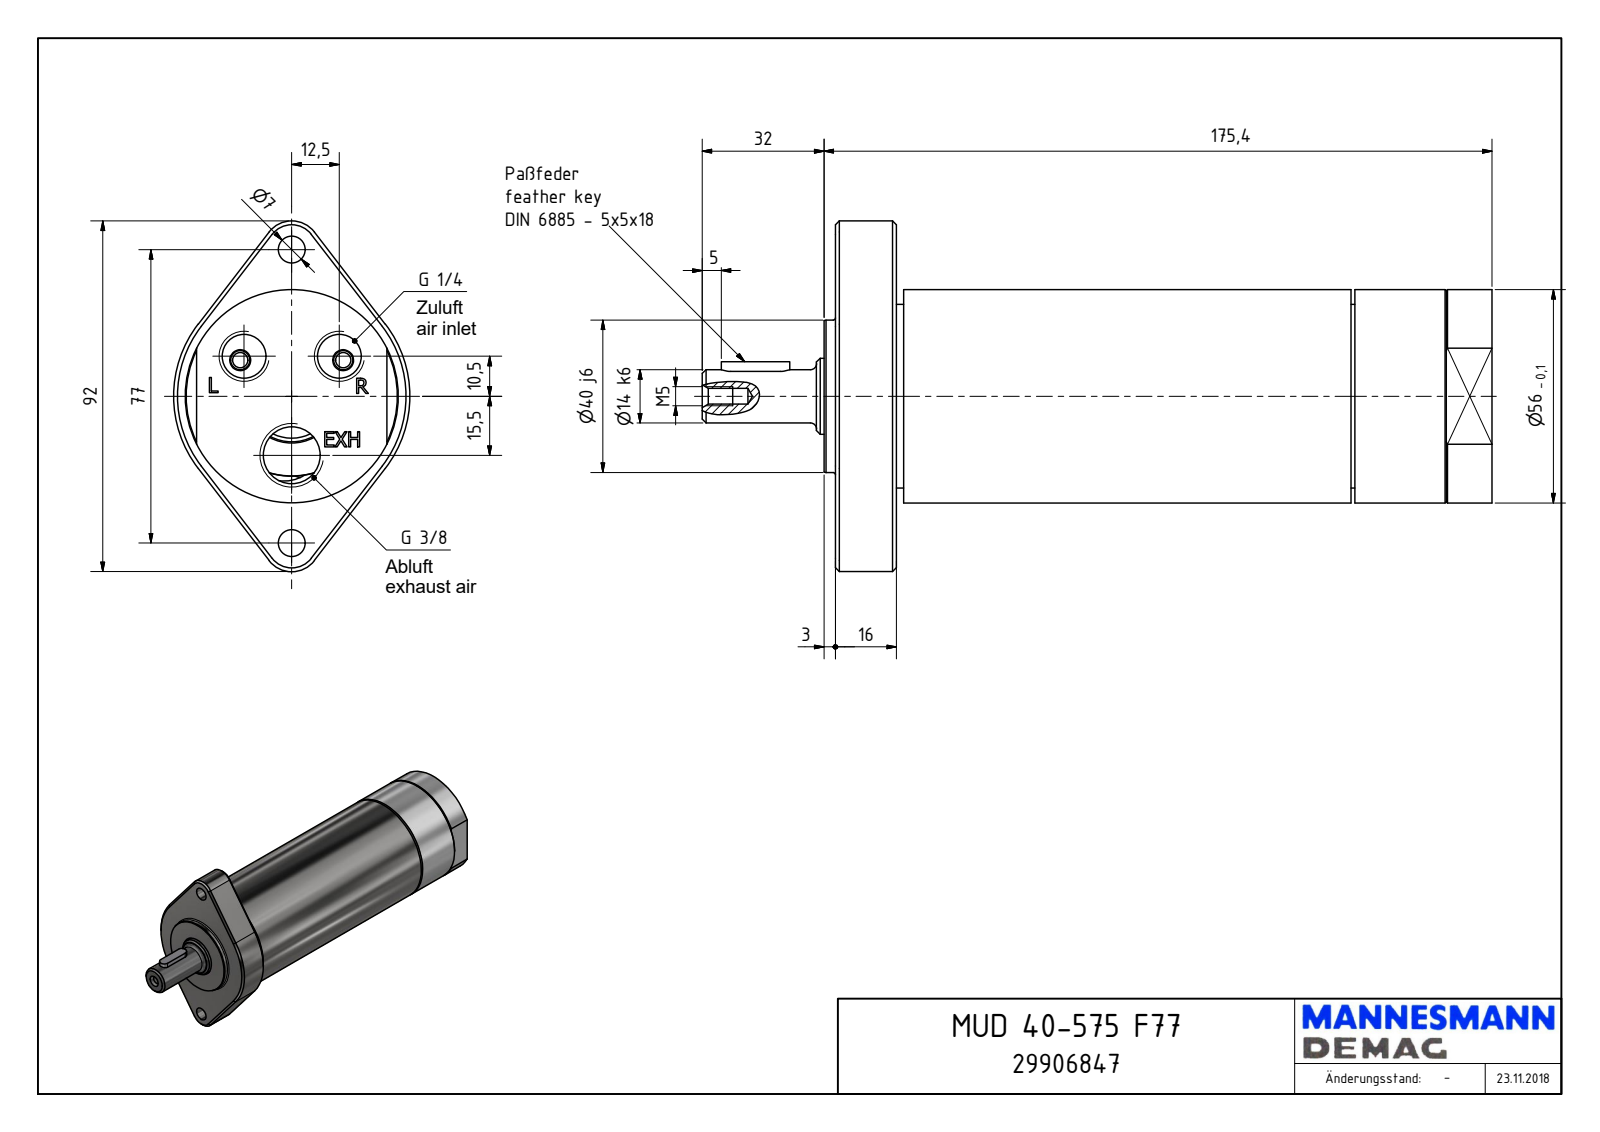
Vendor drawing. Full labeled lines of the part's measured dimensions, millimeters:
Part name (STEP PRODUCT): MUD 40-575 F77_29906847
STEP written by: Autodesk Inventor 2018 (AUTOMOTIVE_DESIGN)
Units: millimetres
Bodies: 1 solid, 175 faces (101 planar, 32 cylindrical, 42 other)
Overall size (bounding box): 207.4 × 92 × 62
Volume: 445 589 mm³ · Surface area: 46 474 mm²
Round holes (diameter × count): ⌀7 ×2, ⌀11.45 ×2, ⌀4.13 ×1, ⌀14.95 ×1, ⌀21 ×1, ⌀21.25 ×1, ⌀26 ×1, ⌀48.38 ×1
Round bosses / shafts (diameter × count): ⌀56 ×1, ⌀48.18 ×1, ⌀40 ×1, ⌀19.95 ×1, ⌀14 ×1
Partial cylindrical surfaces — rounded edges, fillets, slot ends (radius × count): R2.5 ×2, R6 ×2, R7.5 ×2, R21.37 ×1, R23 ×1, R31 ×1
Main face-to-face distances: 172.4, 16, 156.4, 3, 19, 175.4, 20.9, 138.4, 17.9, 135.4
Hole centre spacings: 16.32, 28.85, 30.66, 38.5, 50.57, 15.5, 23, 25
